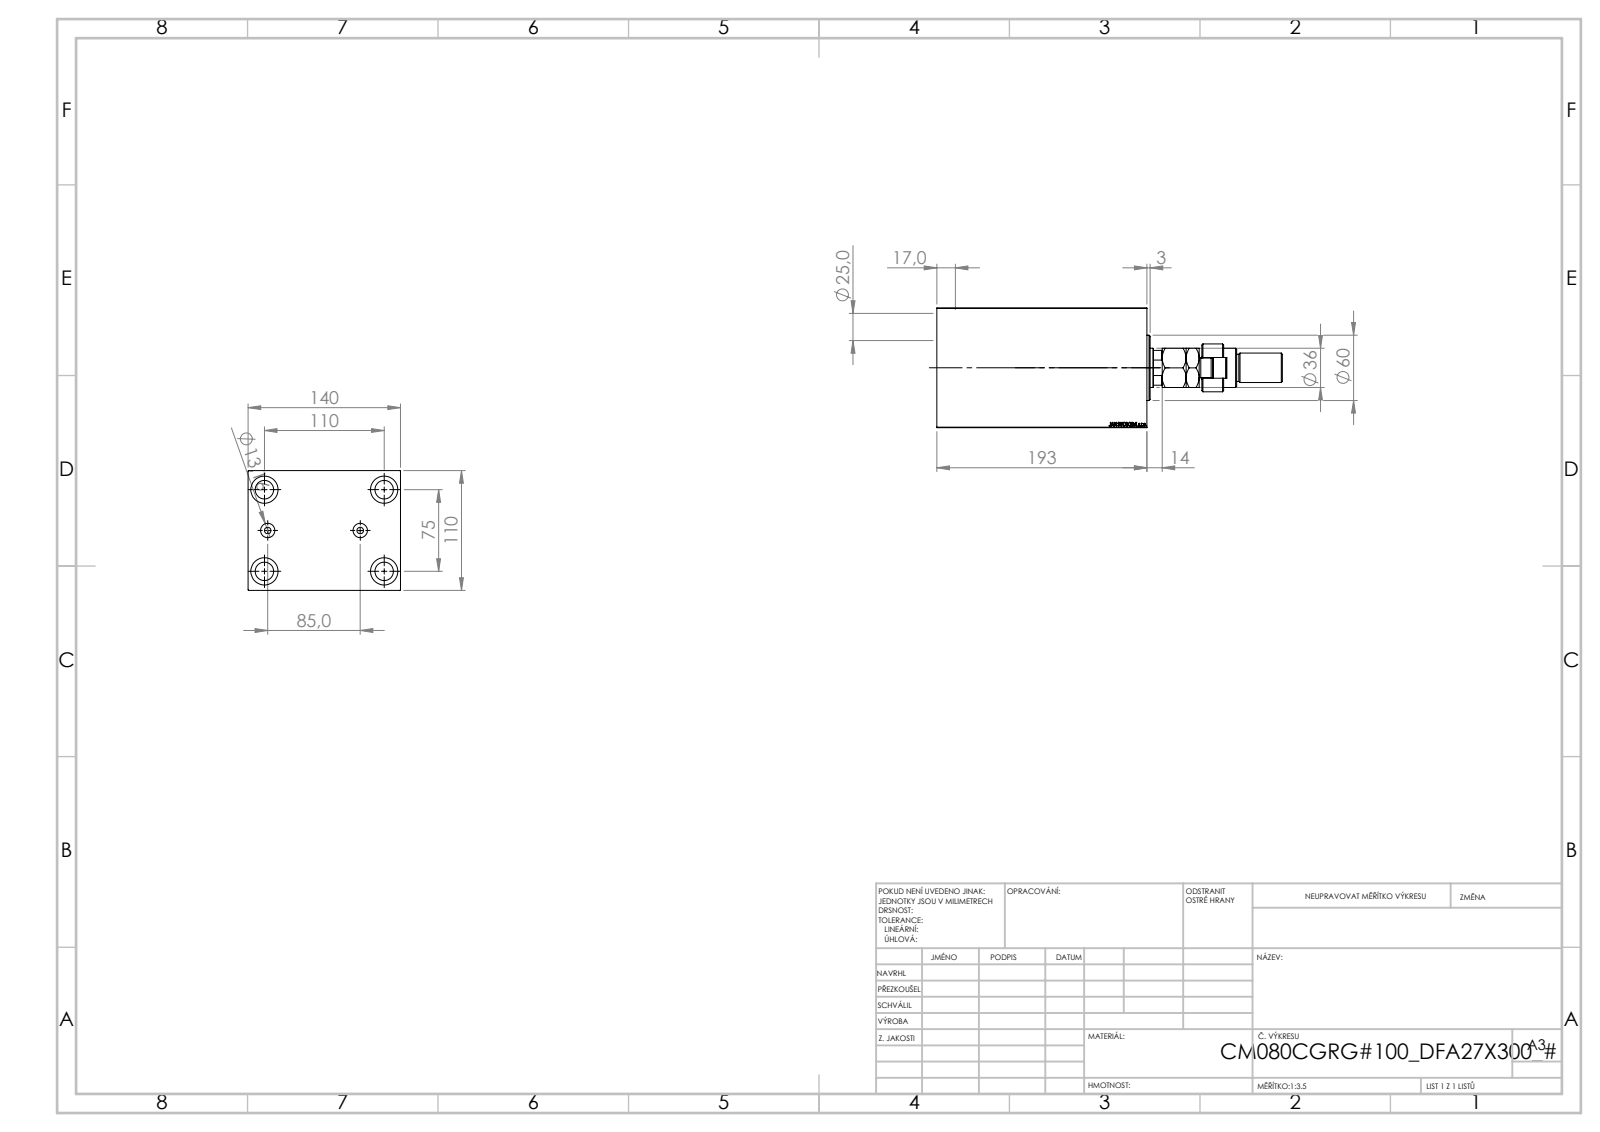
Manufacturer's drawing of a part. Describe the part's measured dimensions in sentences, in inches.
The part is named "V450CM_VC_B; V450CM_C_VCP; FEMALE_PART_FOR_DFA; V450CM_C_Body (+1 more)". Its 3-D file was written by "SolidWorks 2019 (CONFIG_CONTROL_DESIGN)". It is 5 solids with 948 faces: 439 planar, 71 cylindrical and 438 other. Overall it measures 12.5 by 5.512 by 4.331 inches. Its volume is 149.3 cubic inches and its surface area 431.7 square inches. Round holes: 4 of diameter 0.669, 4 of diameter 0.984, 2 of diameter 0.236, 2 of diameter 0.518, 1 of diameter 1.004, 1 of diameter 1.555, 1 of diameter 3.15, 1 of diameter 3.228, 1 of diameter 3.425. Round bosses or shafts: 1 of diameter 2.362, 1 of diameter 1.732, 1 of diameter 1.417, 1 of diameter 1.102, 1 of diameter 1.063, 1 of diameter 0.984, 1 of diameter 0.709. Partial cylindrical surfaces (rounded edges, fillets, slot ends): 1 of radius 0.374, 1 of radius 0.591, 1 of radius 0.689. The main face-to-face distances are 4.331, 5.512, 7.598, 5.344, 2.254, 0.394, 7.205, 3.268, 4.951, 3.937. The hole center spacings are 1.556, 2.621, 4.113, 1.673, 2.953, 4.331, 5.242, 3.346.
